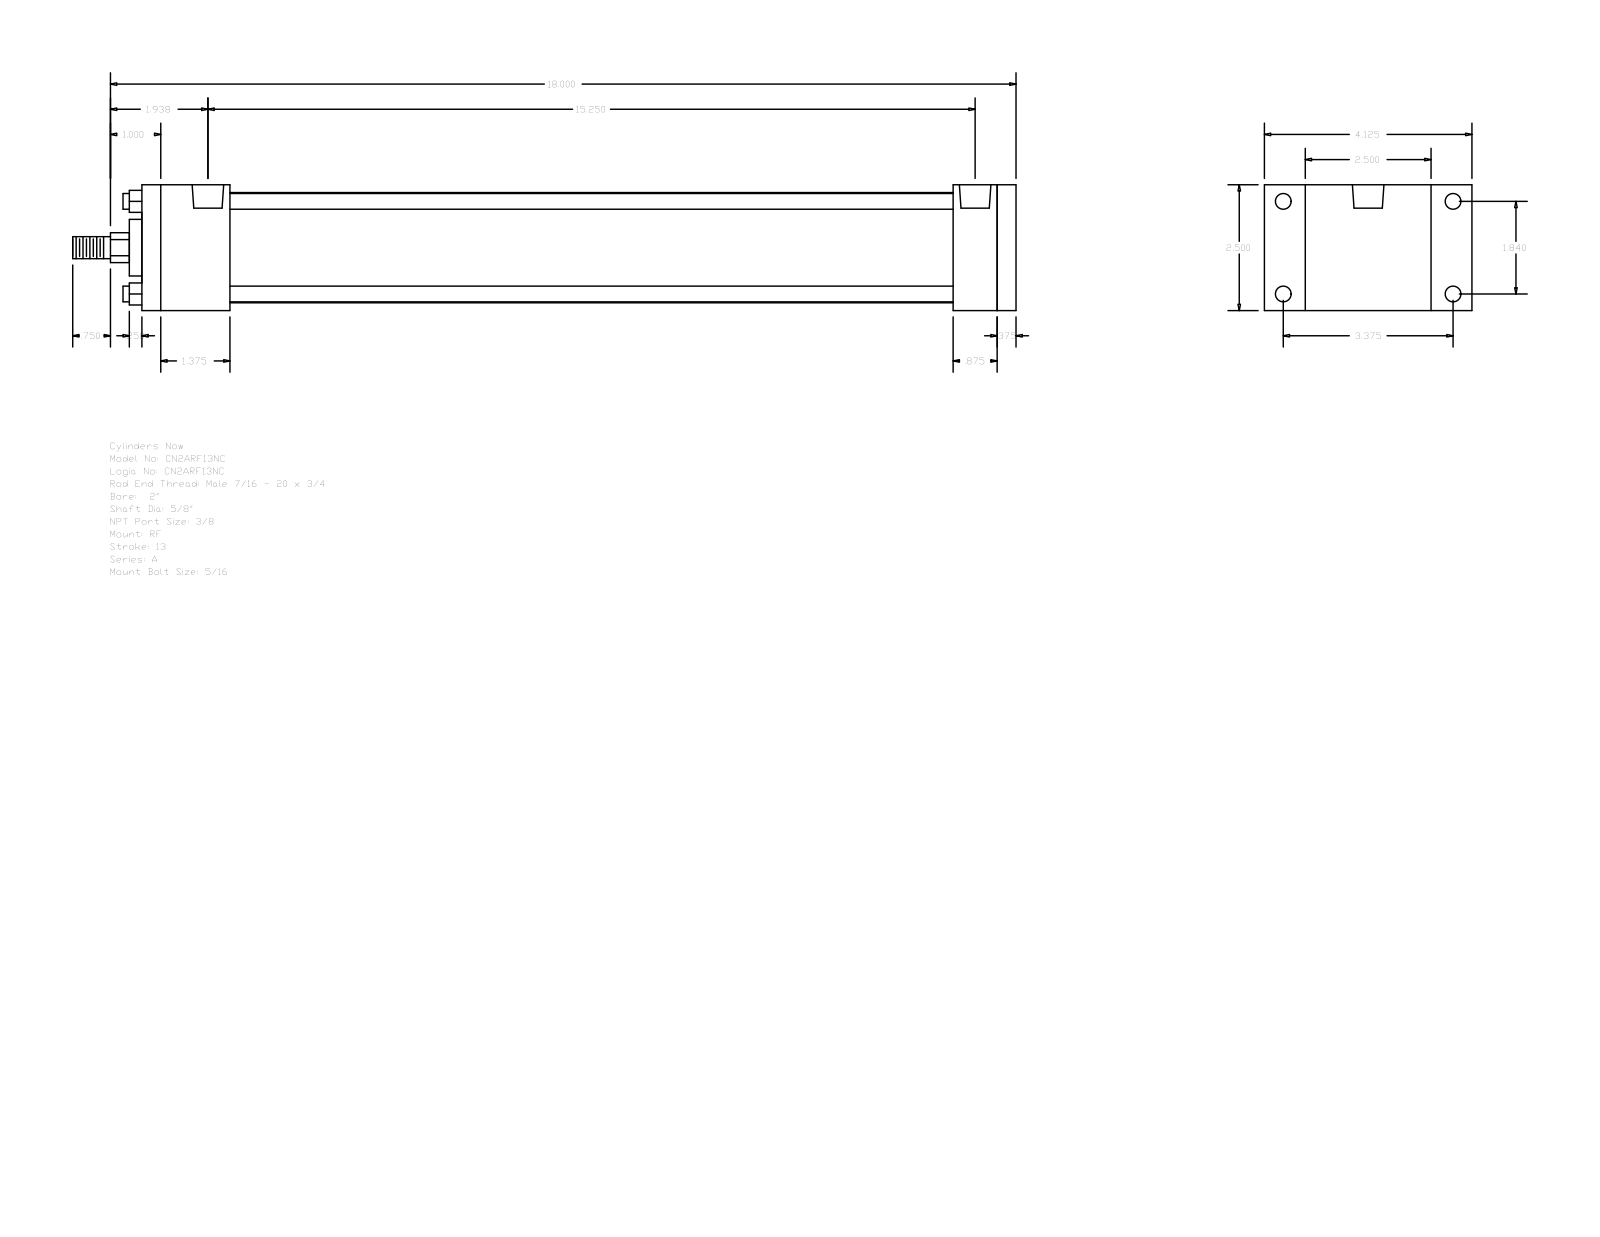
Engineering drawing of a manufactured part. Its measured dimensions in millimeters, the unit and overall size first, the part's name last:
Units: millimetres
Overall size (bounding box): 476.25 × 104.78 × 63.5
Round holes (diameter × count): ⌀5.56 ×4, ⌀7.94 ×4, ⌀15.93 ×2
Round bosses / shafts (diameter × count): ⌀7.94 ×4, ⌀55.63 ×1, ⌀28.57 ×1, ⌀15.88 ×1, ⌀11.11 ×1
Partial cylindrical surfaces — rounded edges, fillets, slot ends (radius × count): R7.54 ×1
Main face-to-face distances: 63.5, 441.32, 431.8, 9.52, 44.45, 387.35, 396.87, 409.57, 365.12, 22.23
Hole centre spacings: 46.74, 85.72, 97.63, 379.4, 3.97, 3.98, 383.37, 383.38
Bodies: 0 solids, 92 faces (64 planar, 28 cylindrical, 0 other)
Part name (STEP PRODUCT): A_RF__0200_0.625
STEP written by: GSSL Pune (CONFIG_CONTROL_DESIGN)
